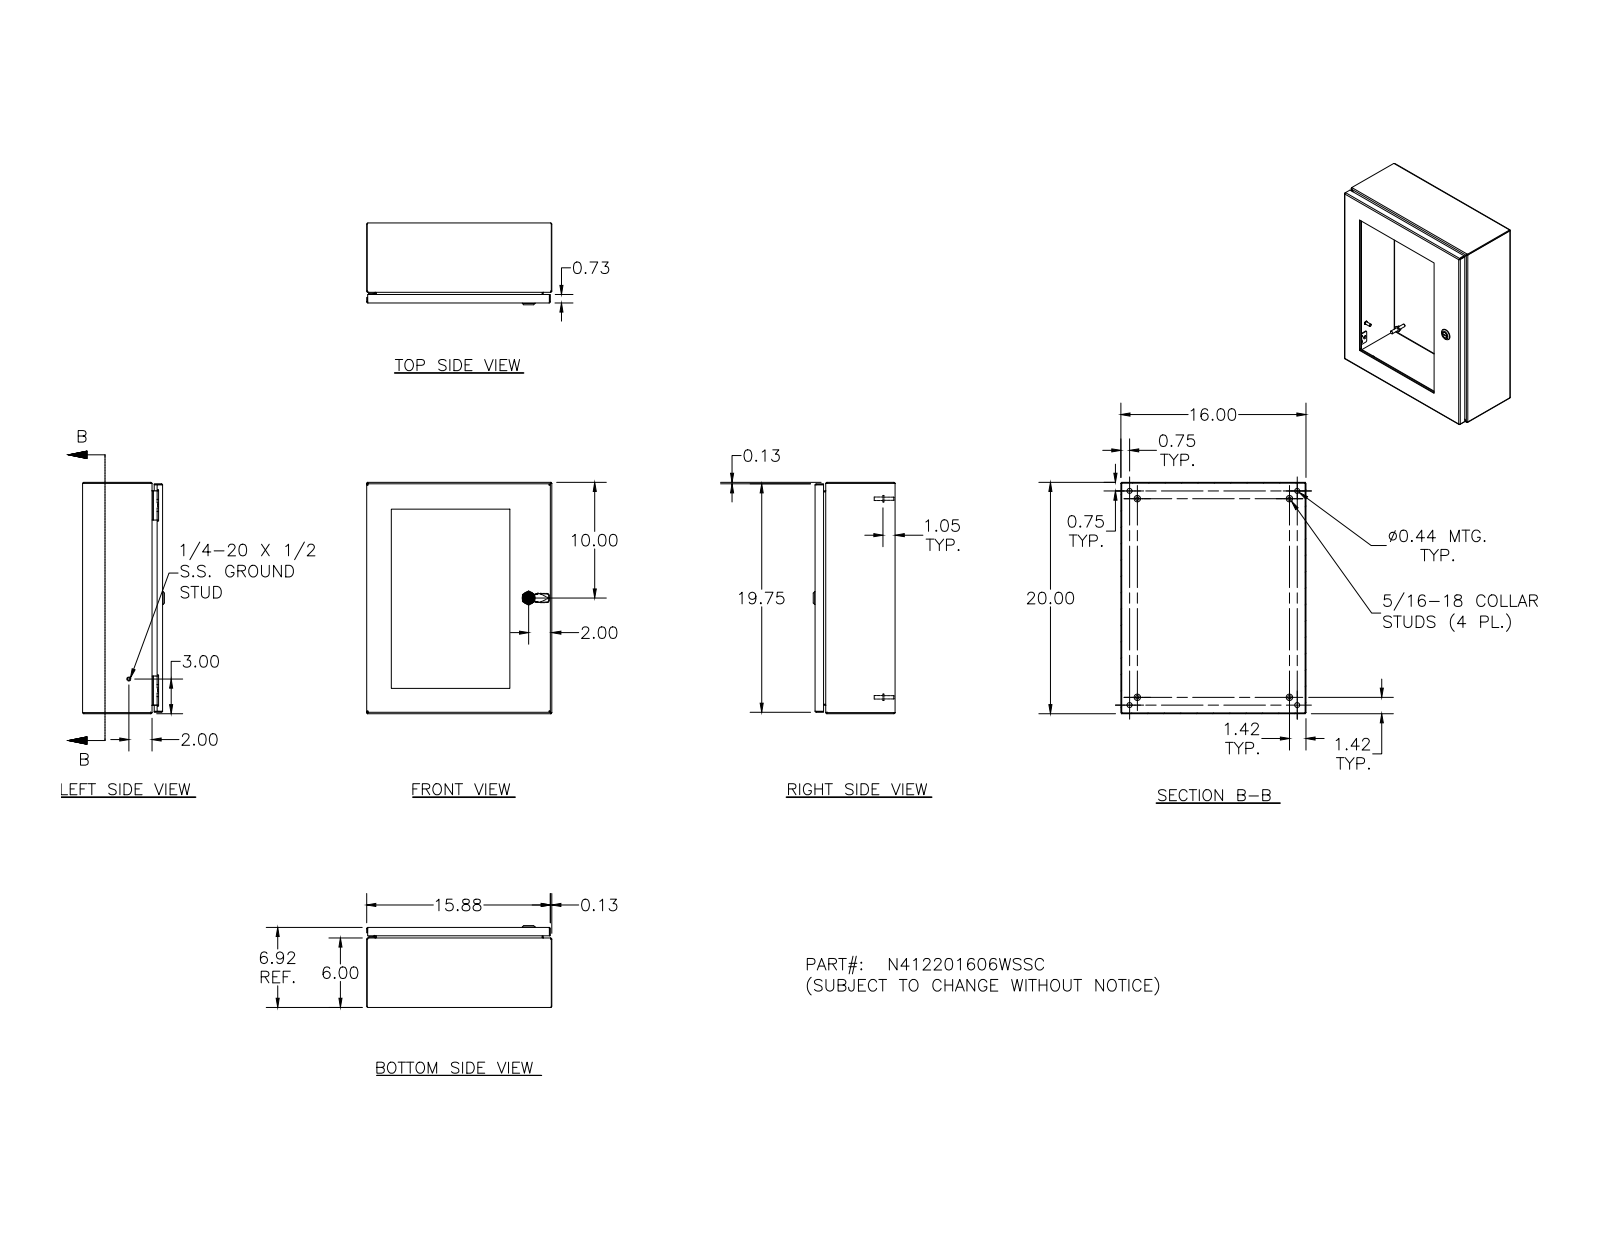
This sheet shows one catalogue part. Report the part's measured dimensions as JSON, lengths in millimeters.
{"part_name": "N412WSSCASSM1PC; N412201606WSSCBKP; N4122016WSSCLID; HFW328176 (+8 more)", "step_written_by": "Autodesk Inventor 2012 (AUTOMOTIVE_DESIGN)", "units": "millimeters", "bodies": {"solids": 66, "faces": 1888, "planar": 732, "cylindrical": 569, "other": 587}, "overall_size": [508, 406.4, 179.7], "volume_mm3": 2125000, "surface_area_mm2": 1722000, "round_holes": [[4, 16], [7.1, 14], [2.4, 4], [3.9, 4], [4.2, 4], [4.4, 4], [4.8, 4], [11.1, 4], [4.7, 1], [5, 1], [8, 1], [10, 1]], "round_bosses_or_shafts": [[4.8, 14], [6.4, 13], [6.4, 10], [14.3, 4], [9.1, 4], [8.1, 4], [7.6, 4], [7, 4]], "partial_cylinders_radius": [[0.8, 34], [1.3, 26], [2.7, 24], [0.4, 18], [3.2, 16], [0.5, 9], [0.8, 8], [1.8, 8]], "face_to_face_distances": [1.9, 173.8, 171.9, 404.5, 6.4, 167.5, 165.6, 506.1, 175.7, 8.2], "hole_center_spacings": [101.6, 203.2, 309.3, 406.4, 158, 218.1, 254.9, 292.1]}
